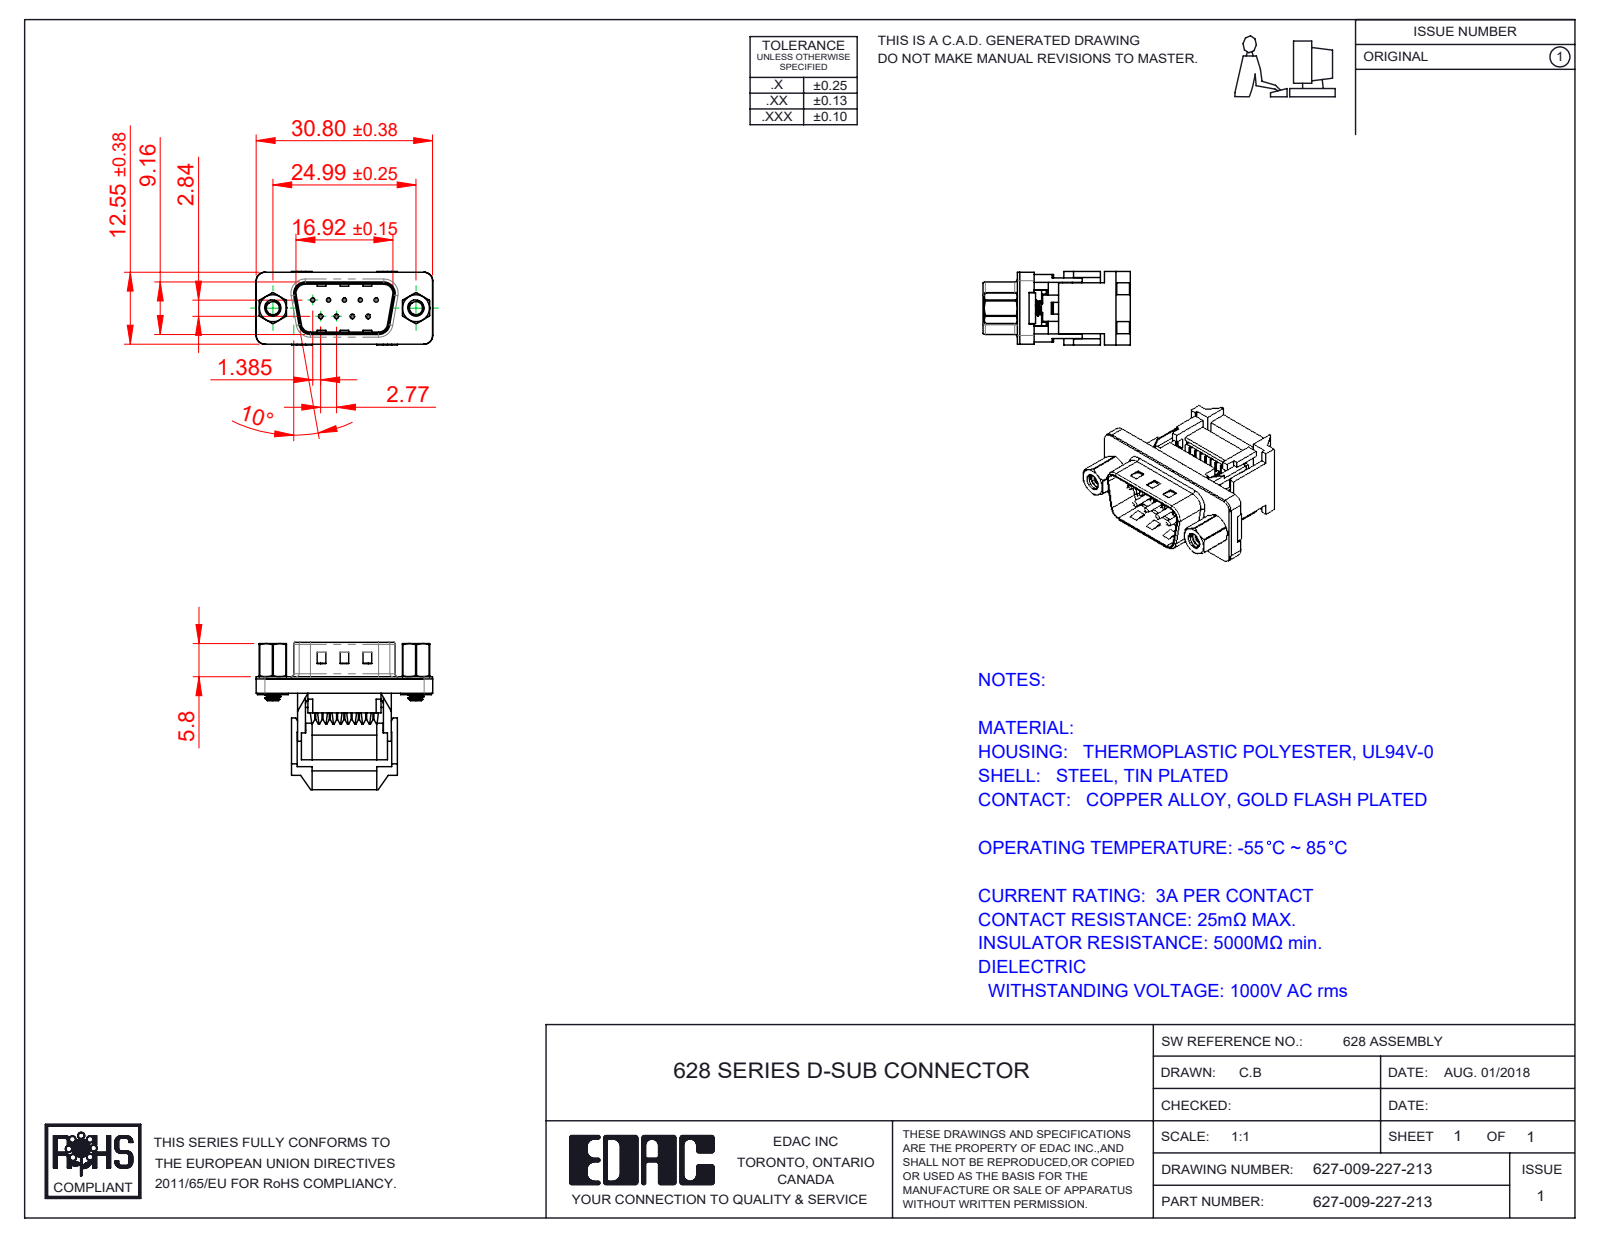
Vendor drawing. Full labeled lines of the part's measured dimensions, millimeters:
Part name (STEP PRODUCT): 627 IDC Housing_09 Contacts; 627 IDC Guide Front_09 Contacts; 627-009-227-213; 627 IDC Contacts_09 Contacts (+5 more)
STEP written by: SolidWorks 2020 (CONFIG_CONTROL_DESIGN)
Units: millimetres
Bodies: 20 solids, 1294 faces (877 planar, 323 cylindrical, 94 other)
Overall size (bounding box): 30.81 × 25.7 × 12.85
Volume: 2 986 mm³ · Surface area: 6 420 mm²
Round holes (diameter × count): ⌀0.75 ×9, ⌀2.26 ×2, ⌀2.29 ×2, ⌀4 ×2, ⌀4.8 ×2, ⌀5 ×2
Round bosses / shafts (diameter × count): ⌀0.75 ×9, ⌀4.9 ×2, ⌀2.79 ×2
Partial cylindrical surfaces — rounded edges, fillets, slot ends (radius × count): R0.5 ×26, R0.65 ×9, R0.89 ×9, R1.5 ×8, R0.3 ×4, R0.9 ×4, R1.6 ×4, R2 ×4
Main face-to-face distances: 0.4, 1, 2.5, 1.9, 1.5, 16.45, 3.15, 2.9, 16.8, 2.6
Hole centre spacings: 2.77, 3.16, 5.54, 3.2, 3.21, 8.31, 5.03, 5.04
